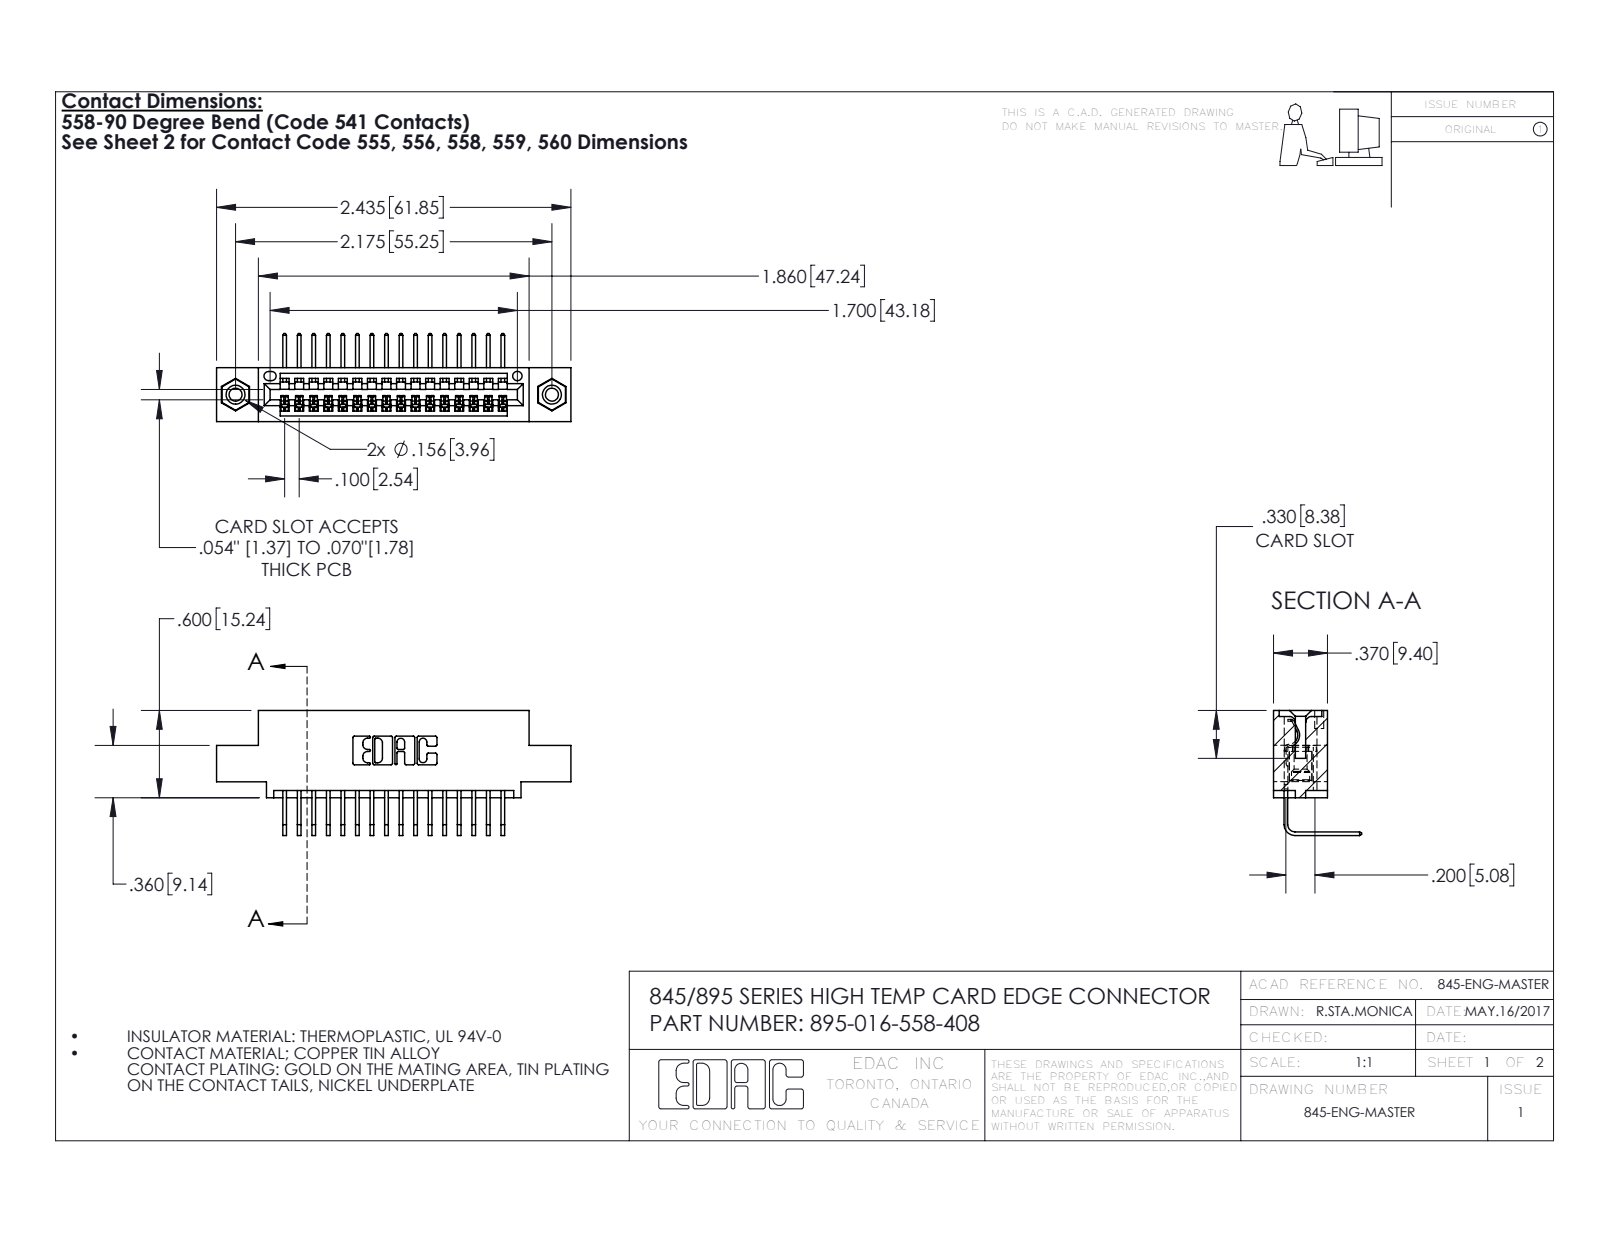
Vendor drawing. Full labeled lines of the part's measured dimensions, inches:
Part name (STEP PRODUCT): 345-250-001_345-250-003-102; 345 Part_0.110 Offset - 0.156 Dia-TI; 395-016-558-408; 345-292-001_558 Tail - 2
STEP written by: SolidWorks 2016 (CONFIG_CONTROL_DESIGN)
Units: inches
Bodies: 19 solids, 1150 faces (788 planar, 346 cylindrical, 16 other)
Overall size (bounding box): 2.435 × 0.859 × 0.605
Volume: 0.344 in³ · Surface area: 11.7 in²
Round holes (diameter × count): ⌀0.089 ×2, ⌀0.125 ×2, ⌀0.156 ×2, ⌀0.064 ×1
Round bosses / shafts (diameter × count): ⌀0.155 ×2
Partial cylindrical surfaces — rounded edges, fillets, slot ends (radius × count): R0.006 ×32, R0.01 ×22, R0.007 ×6, R0.031 ×6, R0.026 ×3, R0.031 ×2, R0.04 ×2, R0.014 ×1
Main face-to-face distances: 0.072, 0.298, 0.37, 0.2, 0.098, 0.272, 0.025, 0.225, 0.1, 0.149
Hole centre spacings: 0.27, 1.942, 2.175
